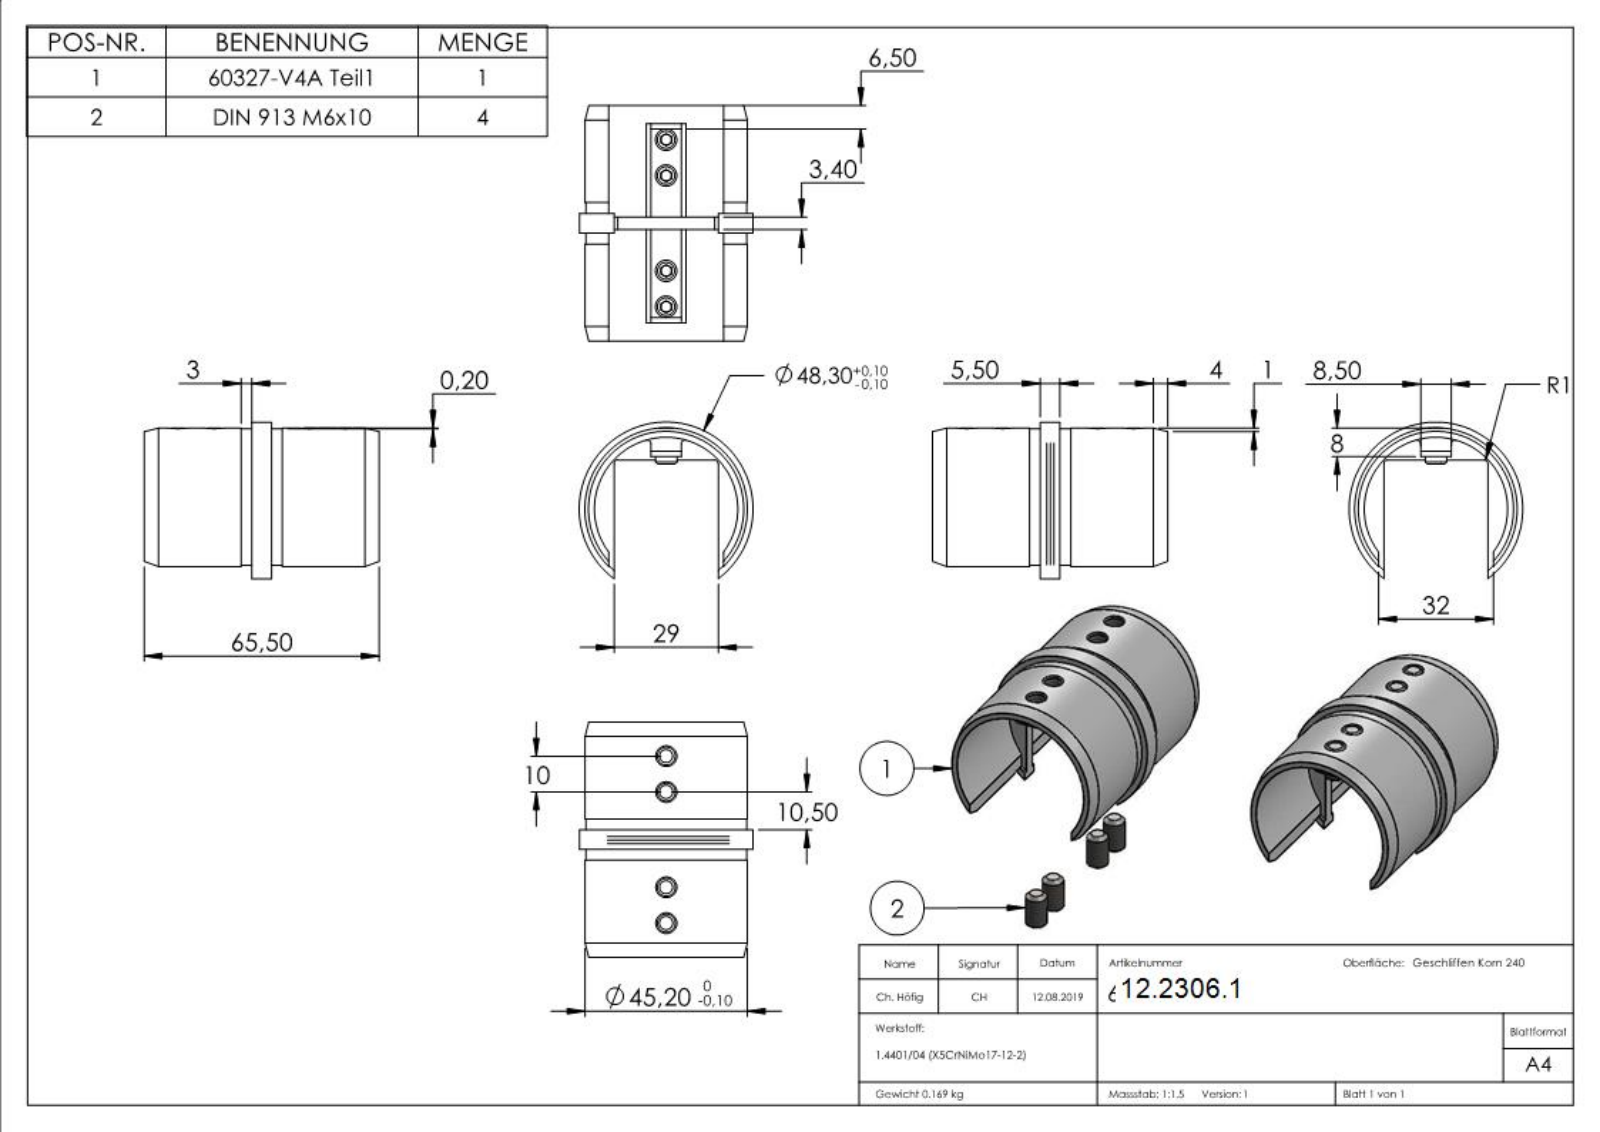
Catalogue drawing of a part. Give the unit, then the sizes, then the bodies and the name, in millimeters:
Units: millimetres
Overall size (bounding box): 65.5 × 48.3 × 43.46
Round holes (diameter × count): ⌀5 ×4
Round bosses / shafts (diameter × count): ⌀6 ×4, ⌀48.3 ×1
Partial cylindrical surfaces — rounded edges, fillets, slot ends (radius × count): R1 ×4, R19.95 ×1, R22.4 ×1, R22.6 ×1
Main face-to-face distances: 1.05, 4.45, 11.75, 20.25, 30, 31.05, 34.45, 35.5, 3.4, 30.5
Hole centre spacings: 10, 36.5, 26.5, 46.5
Volume: 21 163 mm³ · Surface area: 16 568 mm²
Bodies: 5 solids, 381 faces (212 planar, 45 cylindrical, 124 other)
Part name (STEP PRODUCT): 60327-V4A; DIN913_DIN 913 M6x10; 6032X-240 Teil1_60327-V4A Teil1
STEP written by: SolidWorks 2015 (CONFIG_CONTROL_DESIGN)
